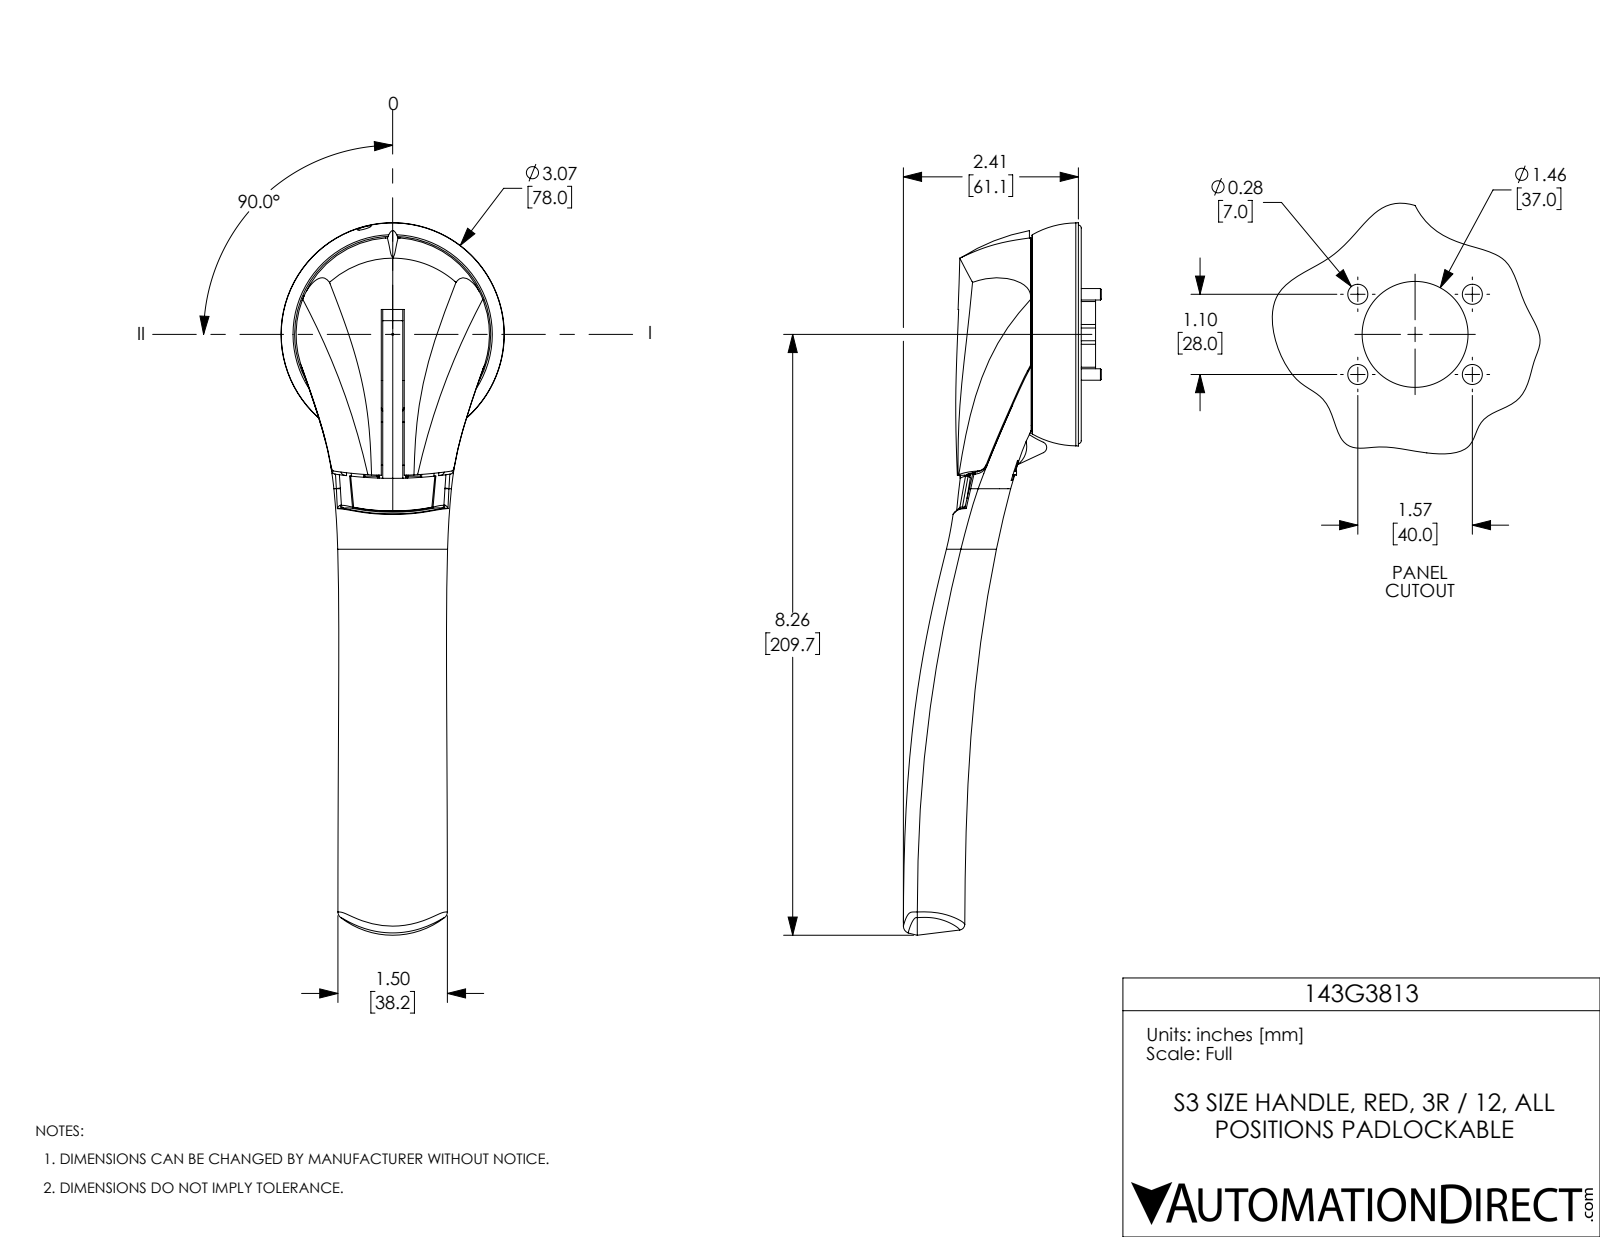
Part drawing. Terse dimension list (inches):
name: 143G3813
written by: SolidWorks 2017 (AUTOMOTIVE_DESIGN)
unit: in
bodies: 8 solids, 1514 faces (806 planar, 544 cylindrical, 164 other)
size: 9.793 × 3.07 × 2.721
volume: 12.91 in³; area: 100.4 in²
holes: 6× ⌀0.157, 4× ⌀0.339, 4× ⌀0.425, 3× ⌀0.03, 2× ⌀0.169, 2× ⌀0.362, 1× ⌀0.118, 1× ⌀0.189, 1× ⌀2.992
bosses: 11× ⌀0.02, 4× ⌀0.335, 4× ⌀0.315, 3× ⌀0.089, 3× ⌀0.069, 2× ⌀0.228, 1× ⌀2.819, 1× ⌀2.701
rounds: 221× R0.01, 20× R0.015, 20× R0.034, 15× R0.03, 4× R0.039, 3× R0.025, 3× R5.437, 2× R0.079
face distances: 0.024, 0.701, 0.713, 0.689, 0.035, 0.276, 0.102, 0.173, 0.244, 0.047
hole spacings: 0.961, 0.309, 0.669, 1.098, 1.102, 1.203, 1.575, 1.881
